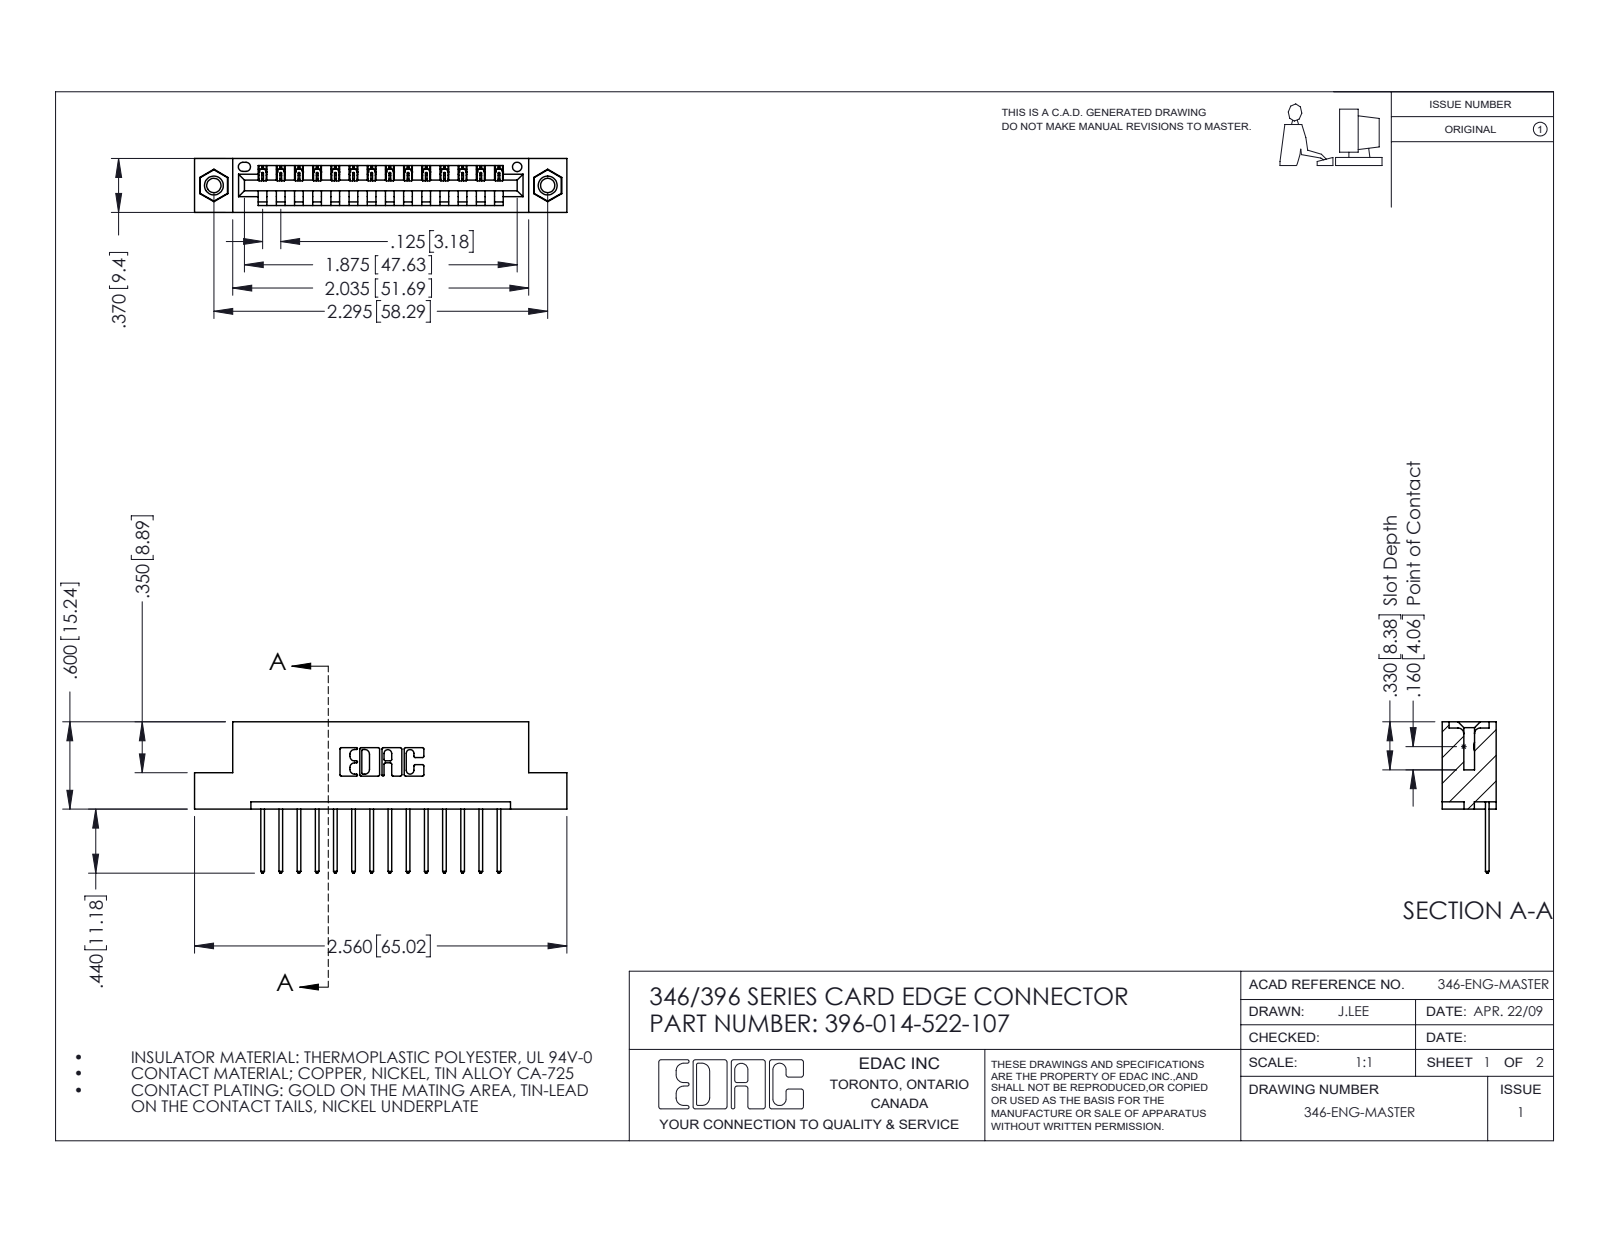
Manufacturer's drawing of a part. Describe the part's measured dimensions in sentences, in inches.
The part is named "396-014-522-107; 346 Part_Flush Mounting Lugs - 0.156 Dia-TI; 345-292-001_345-293-122; 345-250-001_345-250-005-103". Its 3-D file was written by "SolidWorks 2016 (CONFIG_CONTROL_DESIGN)". It is 17 solids with 994 faces: 668 planar, 310 cylindrical and 16 other. Overall it measures 2.56 by 1.04 by 0.37 inches. Its volume is 0.367 cubic inches and its surface area 11.33 square inches. Round holes: 2 of diameter 0.098, 2 of diameter 0.125, 2 of diameter 0.156, 1 of diameter 0.064. Round bosses or shafts: 2 of diameter 0.155. Partial cylindrical surfaces (rounded edges, fillets, slot ends): 28 of radius 0.006, 28 of radius 0.01, 22 of radius 0.01, 6 of radius 0.007, 6 of radius 0.031, 3 of radius 0.026, 2 of radius 0.031, 2 of radius 0.04. The main face-to-face distances are 0.25, 0.048, 0.322, 0.37, 0.072, 0.298, 0.025, 0.148, 0.222, 0.1. The hole center spacings are 0.246, 2.089, 2.295.
